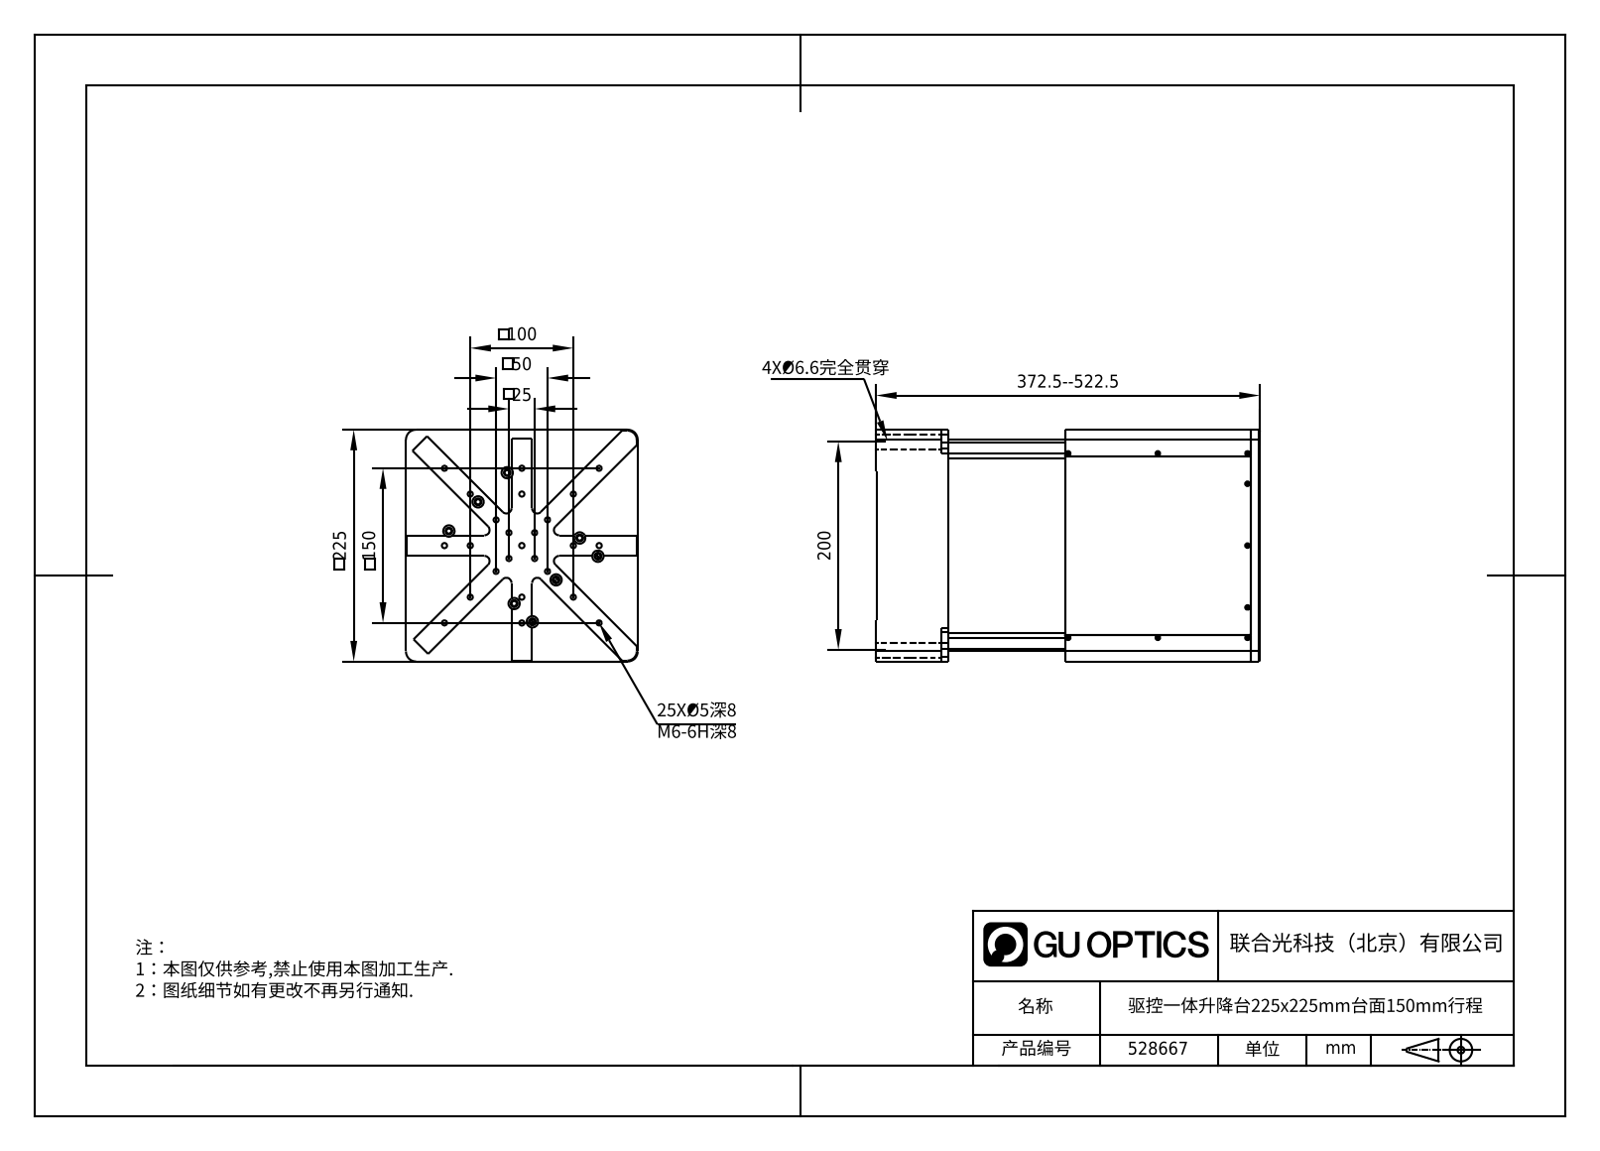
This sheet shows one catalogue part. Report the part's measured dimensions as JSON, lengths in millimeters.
{"part_name": "528667", "step_written_by": "SolidWorks 2020 (CONFIG_CONTROL_DESIGN)", "units": "millimeters", "bodies": {"solids": 0, "faces": 5133, "planar": 2337, "cylindrical": 1475, "other": 1321}, "overall_size": [372.5, 225, 225], "round_holes": [[5, 54], [3.3, 44], [4.5, 43], [6.6, 32], [8, 32], [1.6, 30], [11, 28], [2.5, 24], [3, 21], [2.4, 18], [3.24, 16], [4, 16]], "round_bosses_or_shafts": [[7, 5], [3.2, 4], [23, 2], [12, 2], [5.6, 2], [32, 1], [30, 1], [25, 1]], "partial_cylinders_radius": [[5, 53], [1, 37], [2, 21], [0.5, 18], [0.7, 16], [1.45, 16], [3, 15], [7, 12]], "face_to_face_distances": [2, 10, 215, 212, 12, 3, 7, 222, 210, 9], "hole_center_spacings": [48.9, 88.45, 101.07, 60, 29.7, 30, 161.81, 87]}
